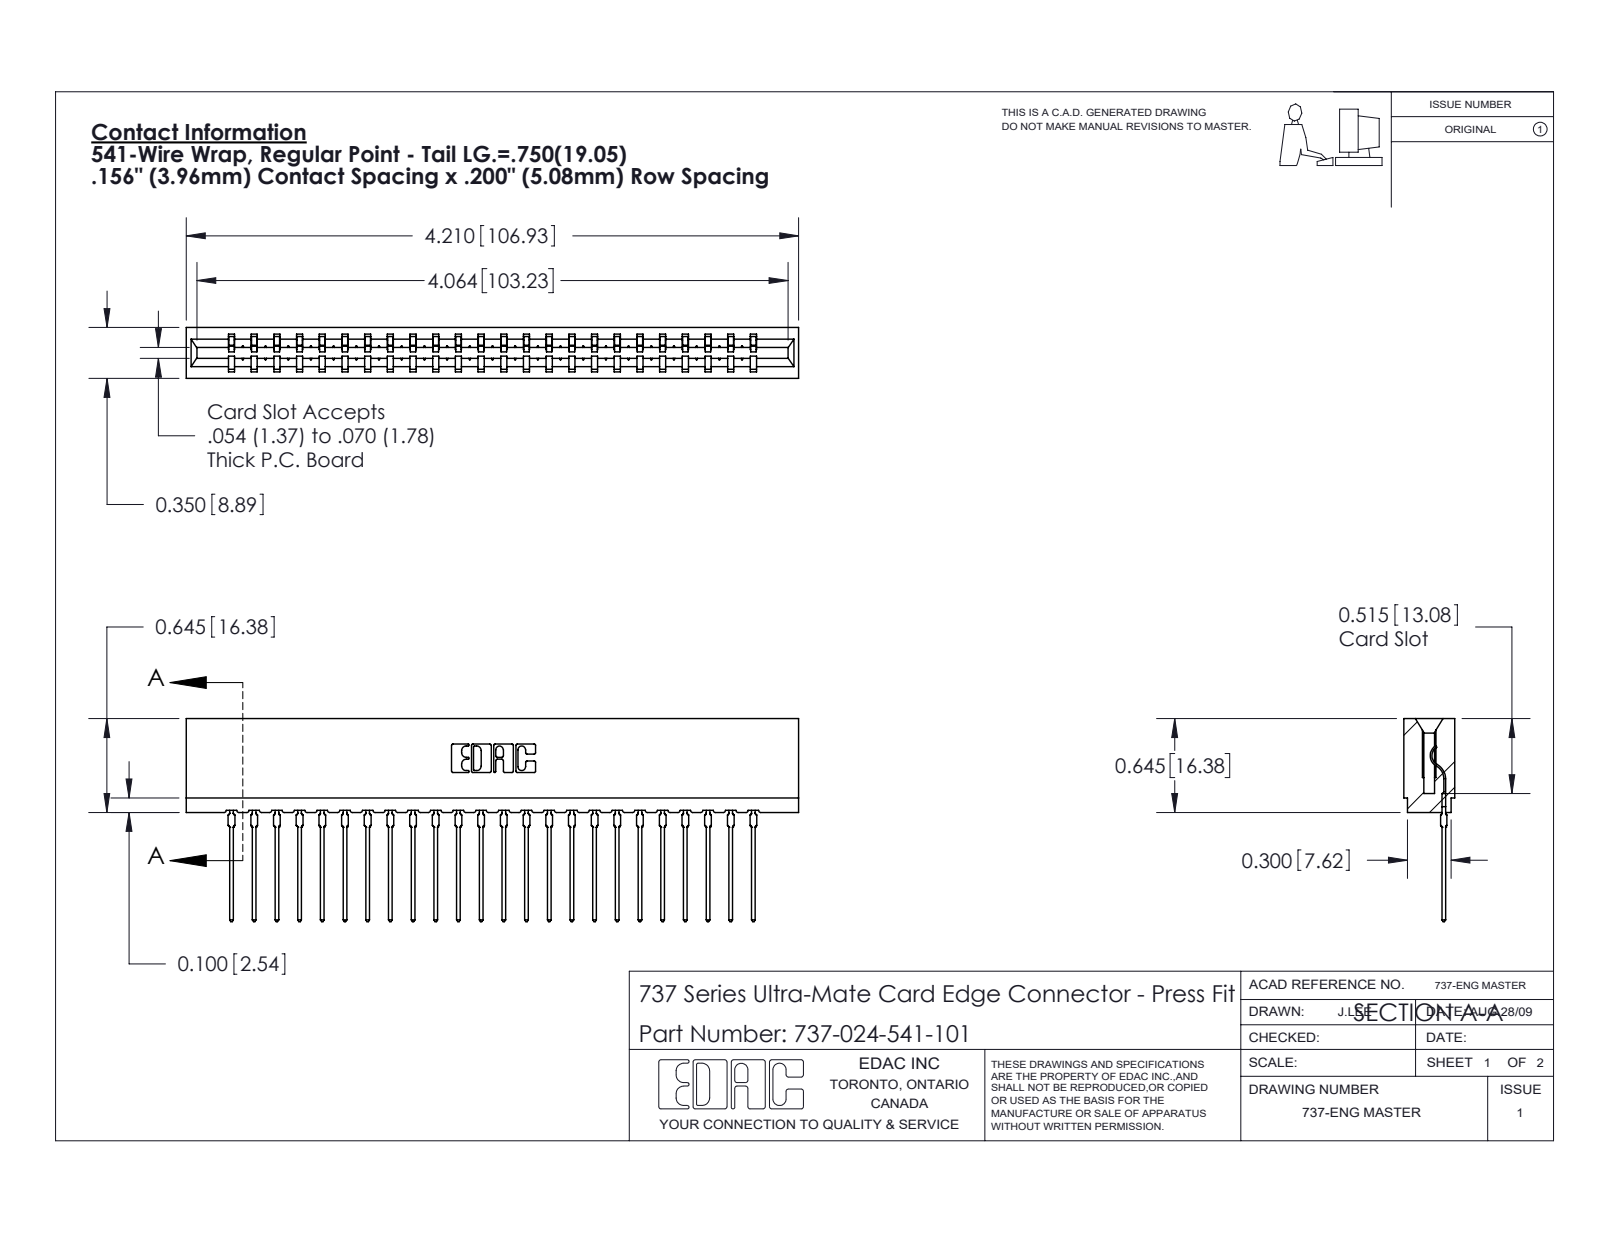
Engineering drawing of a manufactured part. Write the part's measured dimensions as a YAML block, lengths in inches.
part_name: "737-024-541-101; 745-292-001_541; 737 Part_Insulator Option - 01"
step_written_by: "SolidWorks 2020 (CONFIG_CONTROL_DESIGN)"
units: inches
bodies: {solids: 25, faces: 2806, planar: 1686, cylindrical: 496, other: 624}
overall_size: [4.21, 1.396, 0.35]
volume: 0.645
surface_area: 22.29
partial_cylinders:
  - {radius: 0.015, count: 48}
  - {radius: 0.021, count: 48}
  - {radius: 0.01, count: 22}
  - {radius: 0.007, count: 6}
  - {radius: 0.031, count: 6}
  - {radius: 0.005, count: 4}
  - {radius: 0.011, count: 4}
  - {radius: 0.026, count: 3}
face_to_face_distances: [0.138, 0.212, 0.35, 0.074, 0.624, 0.156, 0.063, 0.287, 0.076, 0.149]
